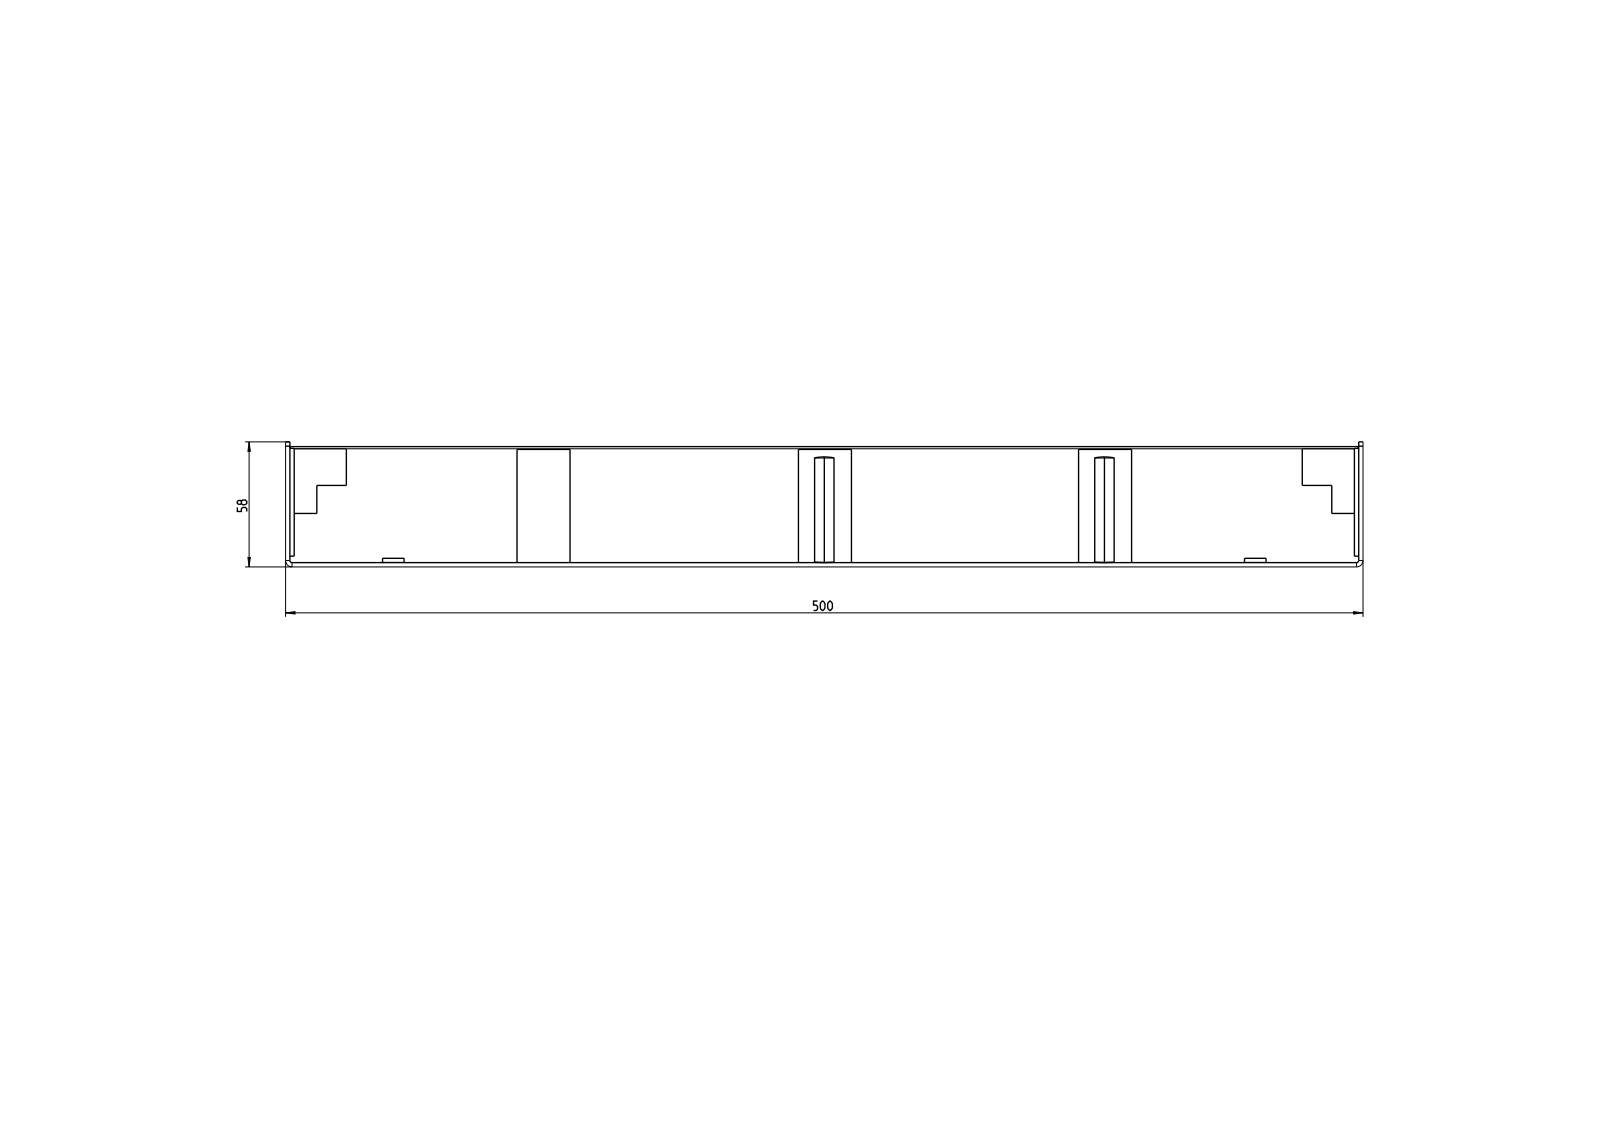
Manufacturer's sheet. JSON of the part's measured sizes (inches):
{"part_name": "T-01020; T-01024; T-01025_AF0; T-01026_ASM (+6 more)", "step_written_by": "CREO PARAMETRIC BY PTC INC, 2022024 (AUTOMOTIVE_DESIGN)", "units": "inches", "bodies": {"solids": 20, "faces": 617, "planar": 442, "cylindrical": 117, "other": 58}, "overall_size": [78.74, 19.685, 2.293], "volume_in3": 590.1, "surface_area_in2": 9591, "round_holes": [[0.535, 13], [0.236, 8], [0.335, 8]], "round_bosses_or_shafts": [[0.394, 8]], "partial_cylinders_radius": [[0.004, 26], [0.039, 2], [0.118, 2]], "face_to_face_distances": [0.079, 2.079, 0.039, 2.118, 2.157, 2.197, 19.528, 19.449, 0.157, 19.606], "hole_center_spacings": [15.748, 23.622, 28.39, 47.244, 0.787, 15.768, 31.496, 49.8]}
